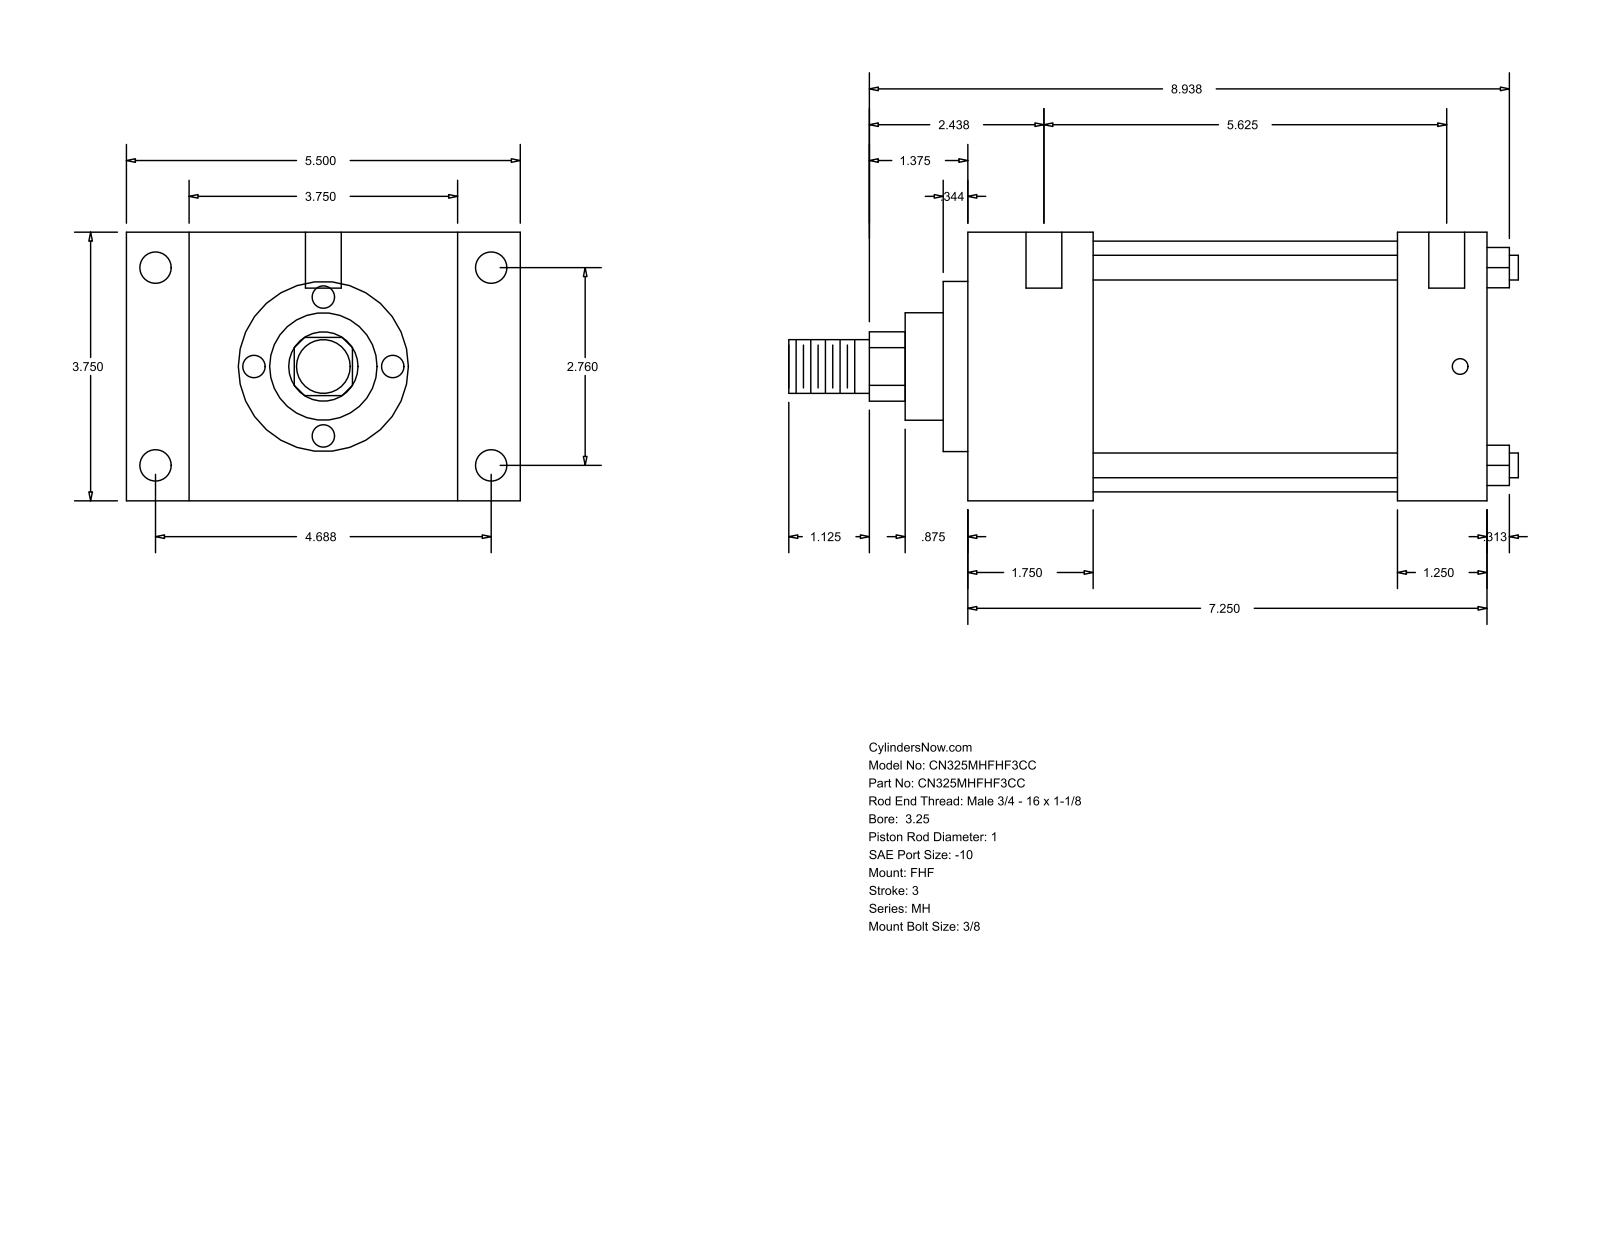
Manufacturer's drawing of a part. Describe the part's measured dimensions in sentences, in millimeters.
The part is named "MH_FHF__0325_1". Its 3-D file was written by "GSSL Pune (CONFIG_CONTROL_DESIGN)". It is 0 solids with 90 faces: 61 planar, 29 cylindrical and 0 other. Overall it measures 258.76 by 139.7 by 95.25 millimeters. Round holes: 4 of diameter 5.56, 4 of diameter 11.13, 2 of diameter 12.7. Round bosses or shafts: 4 of diameter 8.76, 1 of diameter 88.9, 1 of diameter 60.33, 1 of diameter 38.1, 1 of diameter 25.4, 1 of diameter 19.05. Partial cylindrical surfaces (rounded edges, fillets, slot ends): 1 of radius 12.29. The main face-to-face distances are 95.24, 184.15, 44.46, 139.69, 22.23, 117.47, 139.7, 152.4, 107.94, 31.75. The hole center spacings are 70.1, 119.06, 138.16, 149.22, 1.58, 4.76, 142.88, 144.46.
